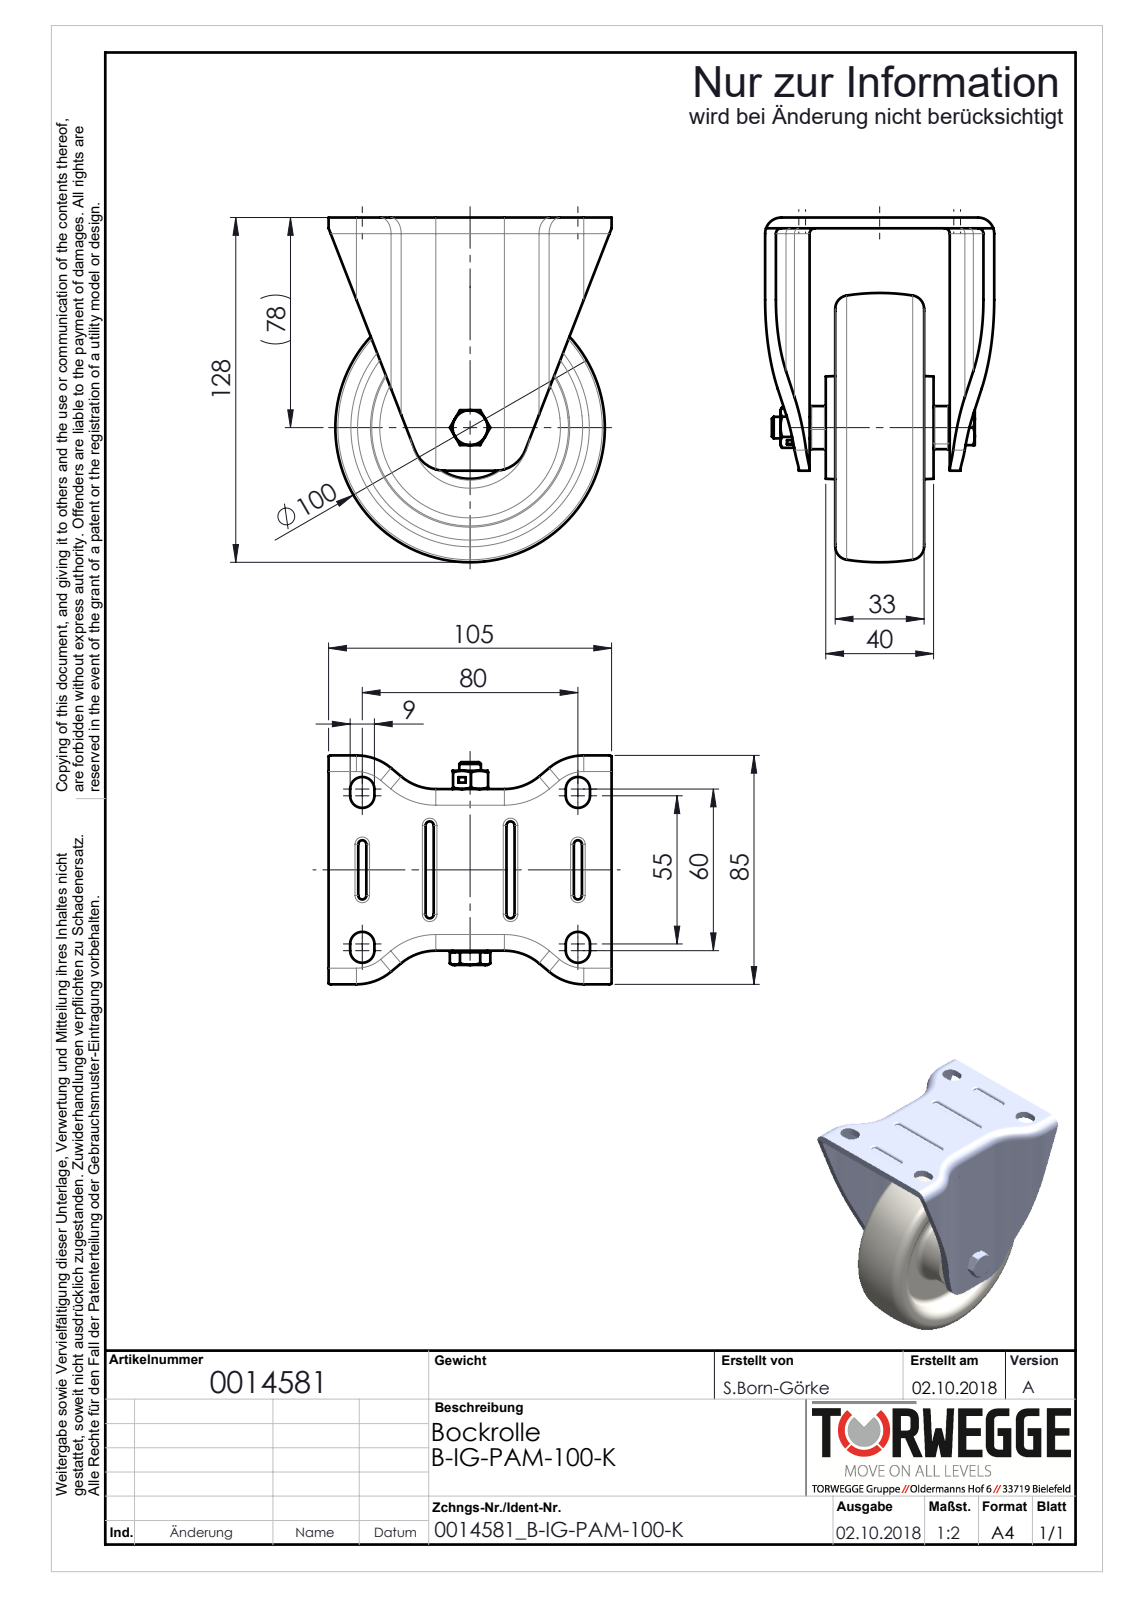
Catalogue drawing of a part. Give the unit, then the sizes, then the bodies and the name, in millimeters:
Units: millimetres
Overall size (bounding box): 128 × 105 × 85
Round holes (diameter × count): ⌀6.8 ×1, ⌀8 ×1, ⌀8.2 ×1, ⌀8.3 ×1, ⌀12 ×1, ⌀12.4 ×1, ⌀16.8 ×1, ⌀23 ×1, ⌀23.2 ×1
Round bosses / shafts (diameter × count): ⌀28 ×1, ⌀16 ×1, ⌀15 ×1, ⌀13 ×1
Partial cylindrical surfaces — rounded edges, fillets, slot ends (radius × count): R1.2 ×8, R2 ×8, R4.5 ×8, R6 ×8, R20 ×8, R16 ×4, R24 ×4, R12 ×2
Main face-to-face distances: 4, 25, 56, 35, 21, 31, 10, 60, 52, 50
Volume: 264 996 mm³ · Surface area: 92 891 mm²
Bodies: 13 solids, 360 faces (110 planar, 126 cylindrical, 124 other)
Part name (STEP PRODUCT): 0014581_B-IG-PAM-100-K
STEP written by: SolidWorks 2018 (AUTOMOTIVE_DESIGN)
